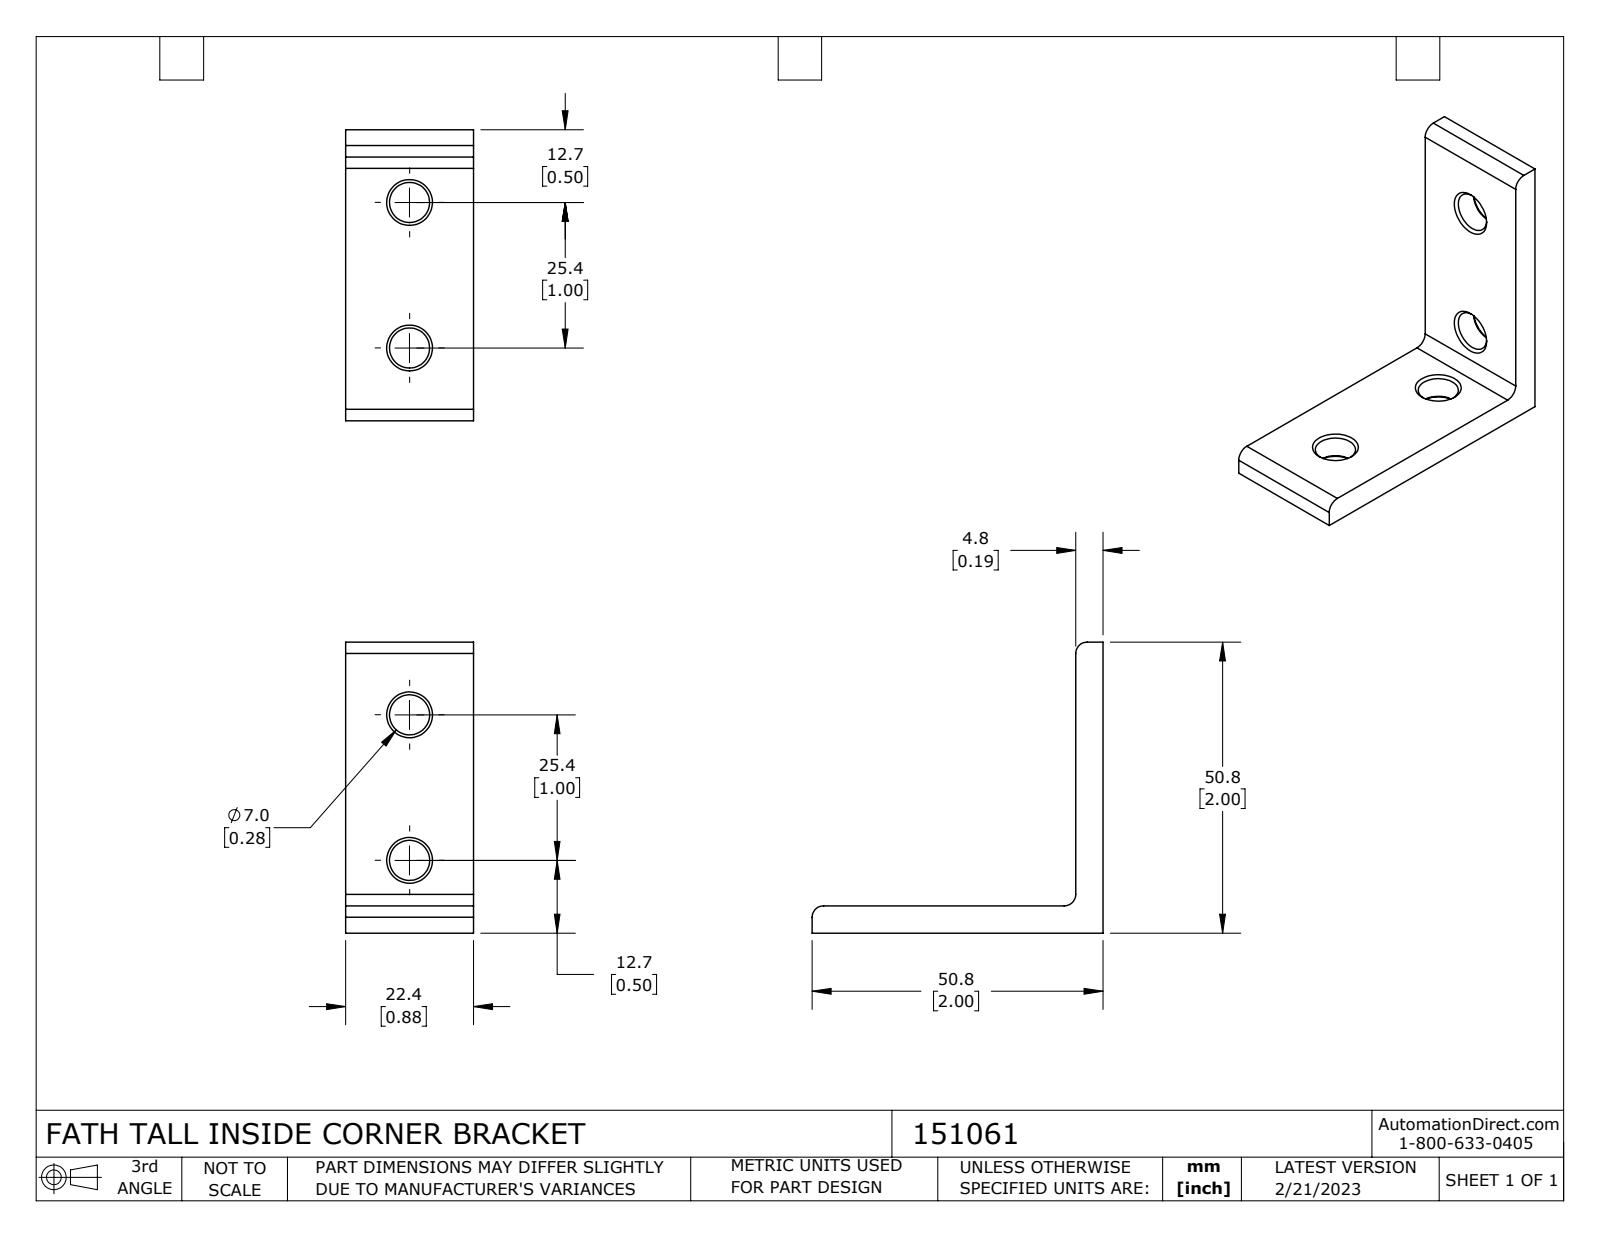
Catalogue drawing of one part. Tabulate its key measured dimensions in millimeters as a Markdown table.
| quantity | value |
| --- | --- |
| part name | 151061 |
| STEP written by | SolidWorks 2021 (CONFIG_CONTROL_DESIGN) |
| units | millimeters |
| bodies | 1 solid, 35 faces (8 planar, 11 cylindrical, 16 other) |
| overall size | 50.8 × 50.8 × 22.4 |
| volume | 9 540 mm³ |
| surface area | 5 467 mm² |
| round holes (diameter × count) | 7 × 4 |
| partial cylindrical surfaces (radius × count) | 2 × 3 |
| main face-to-face distances | 4.7, 22.4, 50.8, 46.1 |
| hole center spacings | 25.4 |
